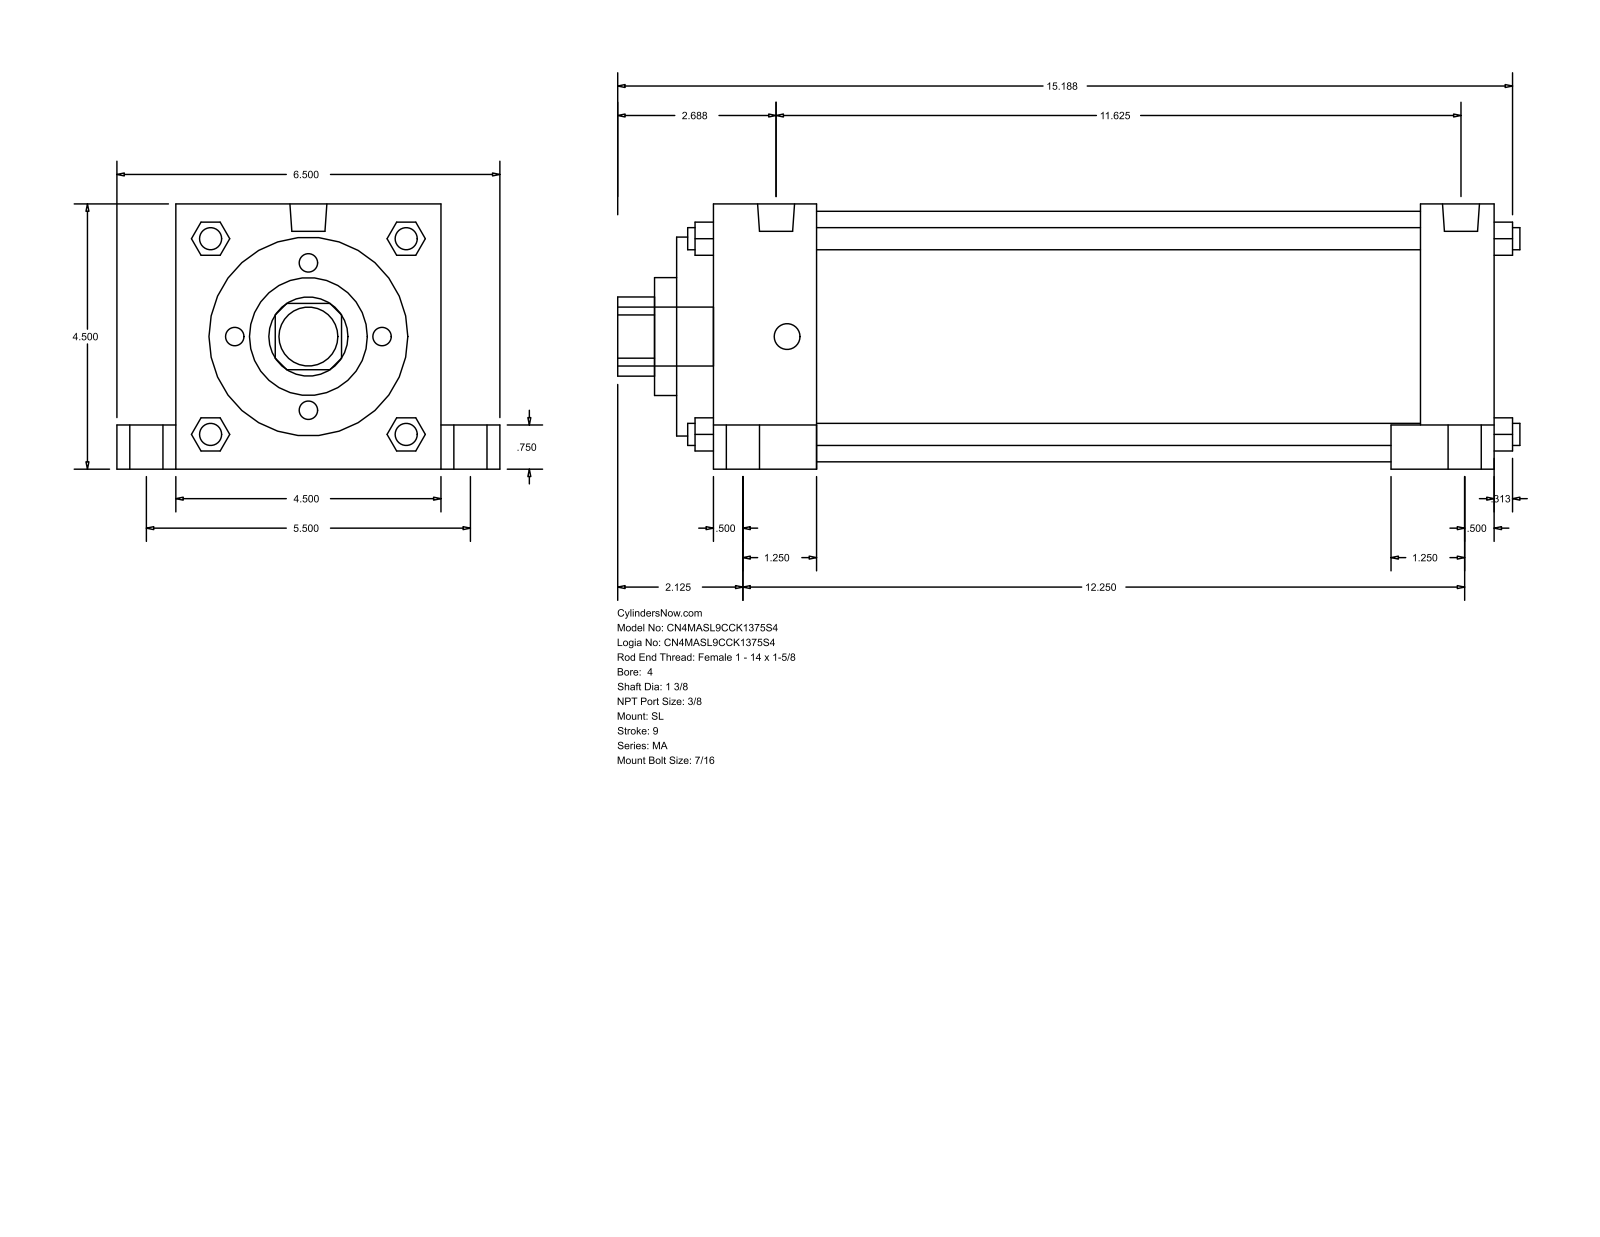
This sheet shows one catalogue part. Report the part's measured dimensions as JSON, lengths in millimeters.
{"part_name": "MA_SL__0400_1.375", "step_written_by": "GSSL Pune (CONFIG_CONTROL_DESIGN)", "units": "millimeters", "bodies": {"solids": 0, "faces": 150, "planar": 113, "cylindrical": 37, "other": 0}, "overall_size": [388.94, 165.1, 114.3], "round_holes": [[34.92, 1], [50.8, 1], [85.72, 1], [107.95, 1]], "round_bosses_or_shafts": [[20.64, 4], [14.29, 4], [11.11, 4], [9.53, 4], [15.93, 2], [25.4, 1]], "partial_cylinders_radius": [[17.06, 1]], "face_to_face_distances": [114.3, 336.55, 260.35, 352.42, 15.87, 60.32, 44.45, 292.1, 320.67, 304.8]}
